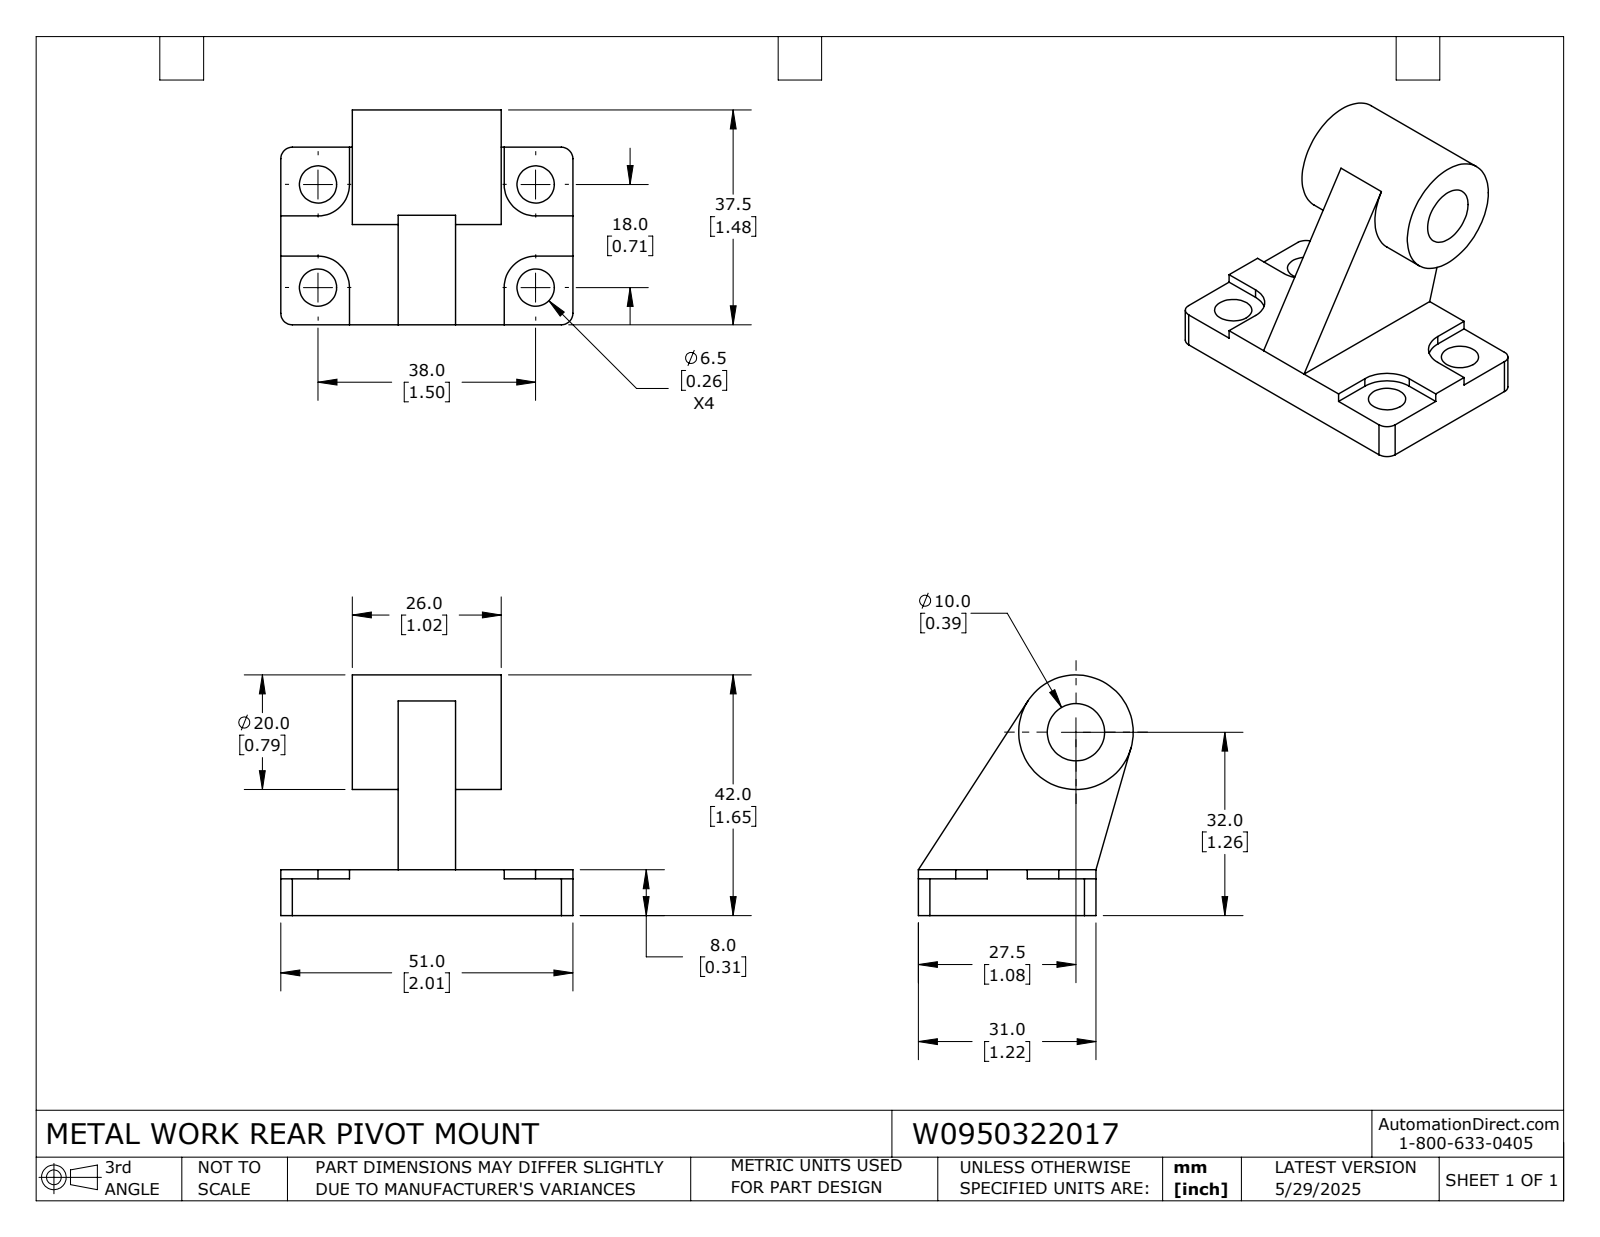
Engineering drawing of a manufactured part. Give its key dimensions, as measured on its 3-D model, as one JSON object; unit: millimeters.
{"part_name": "W0950322017", "step_written_by": "SolidWorks 2024 (CONFIG_CONTROL_DESIGN)", "units": "millimeters", "bodies": {"solids": 1, "faces": 50, "planar": 30, "cylindrical": 20, "other": 0}, "overall_size": [51, 42, 37.5], "volume_mm3": 20561, "surface_area_mm2": 8752, "round_holes": [[6.5, 4], [10, 1]], "round_bosses_or_shafts": [[20, 1]], "partial_cylinders_radius": [[2, 4], [5.5, 4]], "face_to_face_distances": [8, 5, 10, 3, 18, 6.4, 3.4, 1.6, 12.5, 20.5], "hole_center_spacings": [18, 38, 42.05]}
